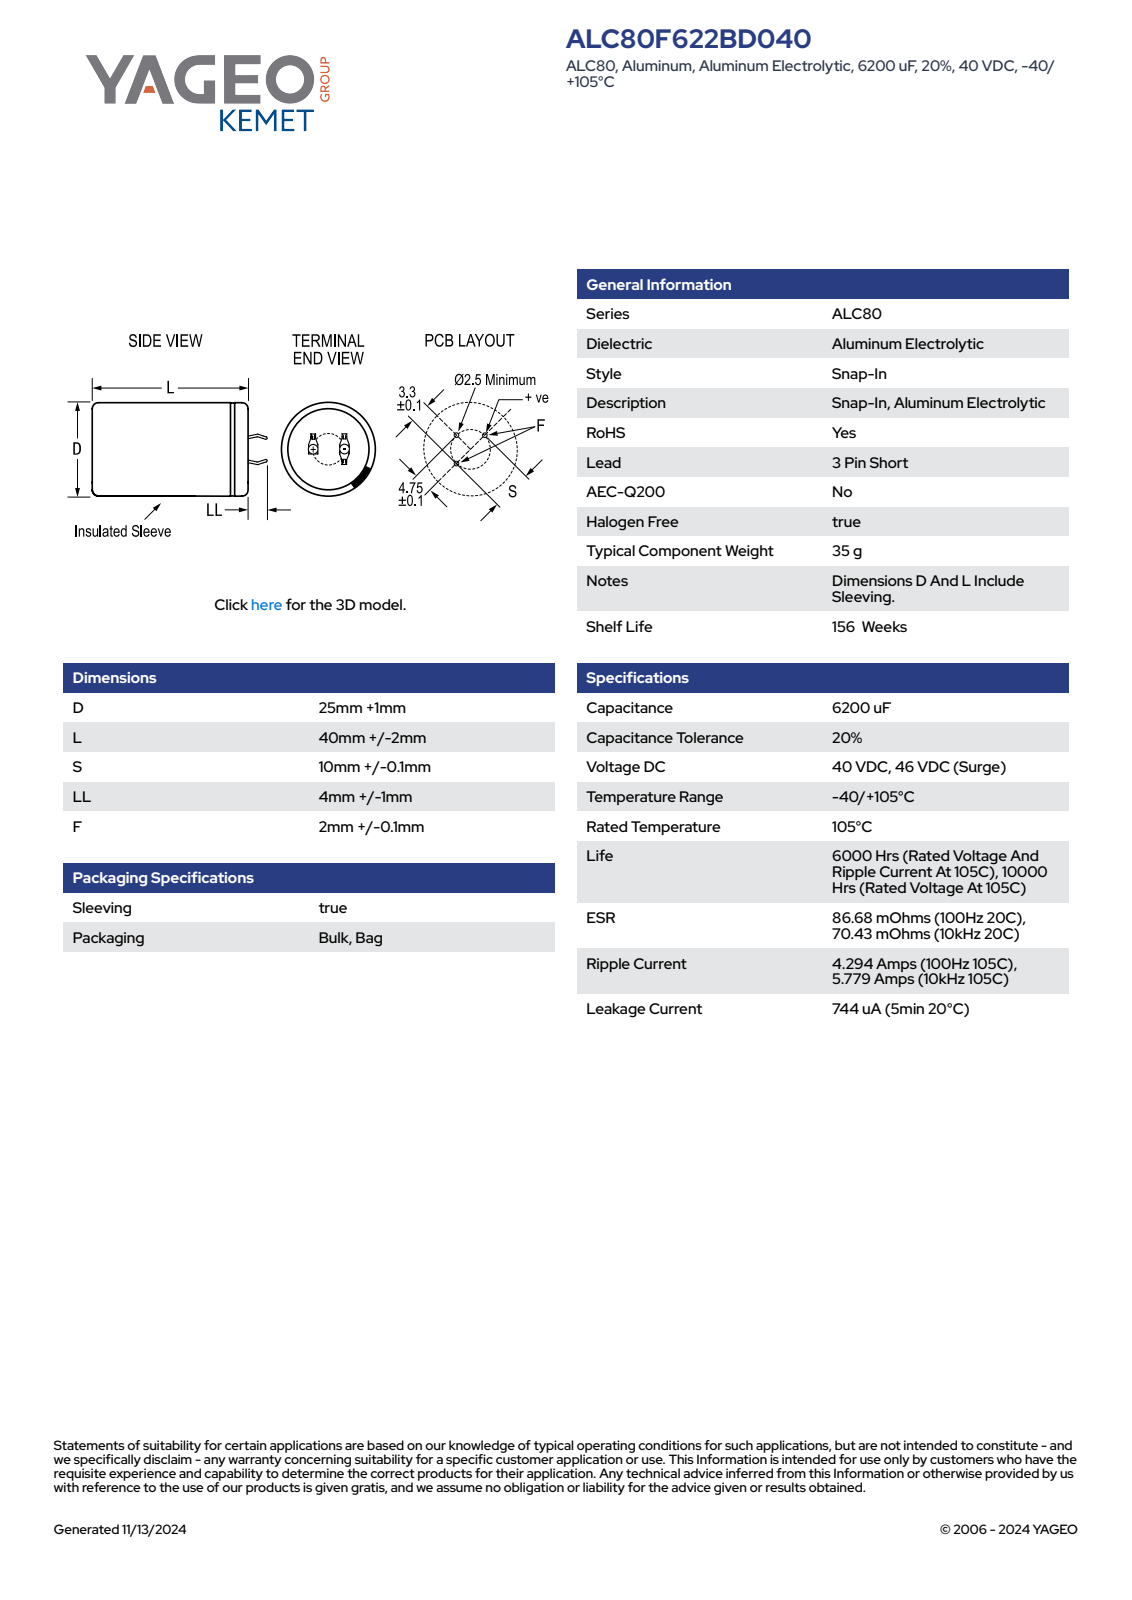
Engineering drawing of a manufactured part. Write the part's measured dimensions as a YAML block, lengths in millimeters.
part_name: "CARS_K3P_25X40_D26L42S10LL5F2.1"
step_written_by: "SolidWorks 2014 (AUTOMOTIVE_DESIGN)"
units: millimeters
bodies: {solids: 1, faces: 115, planar: 61, cylindrical: 15, other: 39}
overall_size: [46.99, 26, 26]
volume: 22107
surface_area: 4513
round_holes:
  - {diameter: 23, count: 1}
round_bosses_or_shafts:
  - {diameter: 26, count: 1}
partial_cylinders:
  - {radius: 12.99, count: 1}
face_to_face_distances: [41.99, 42.49, 0.5, 0.6, 8.22, 0.75, 1.35, 0.59, 0.58, 7.47]
